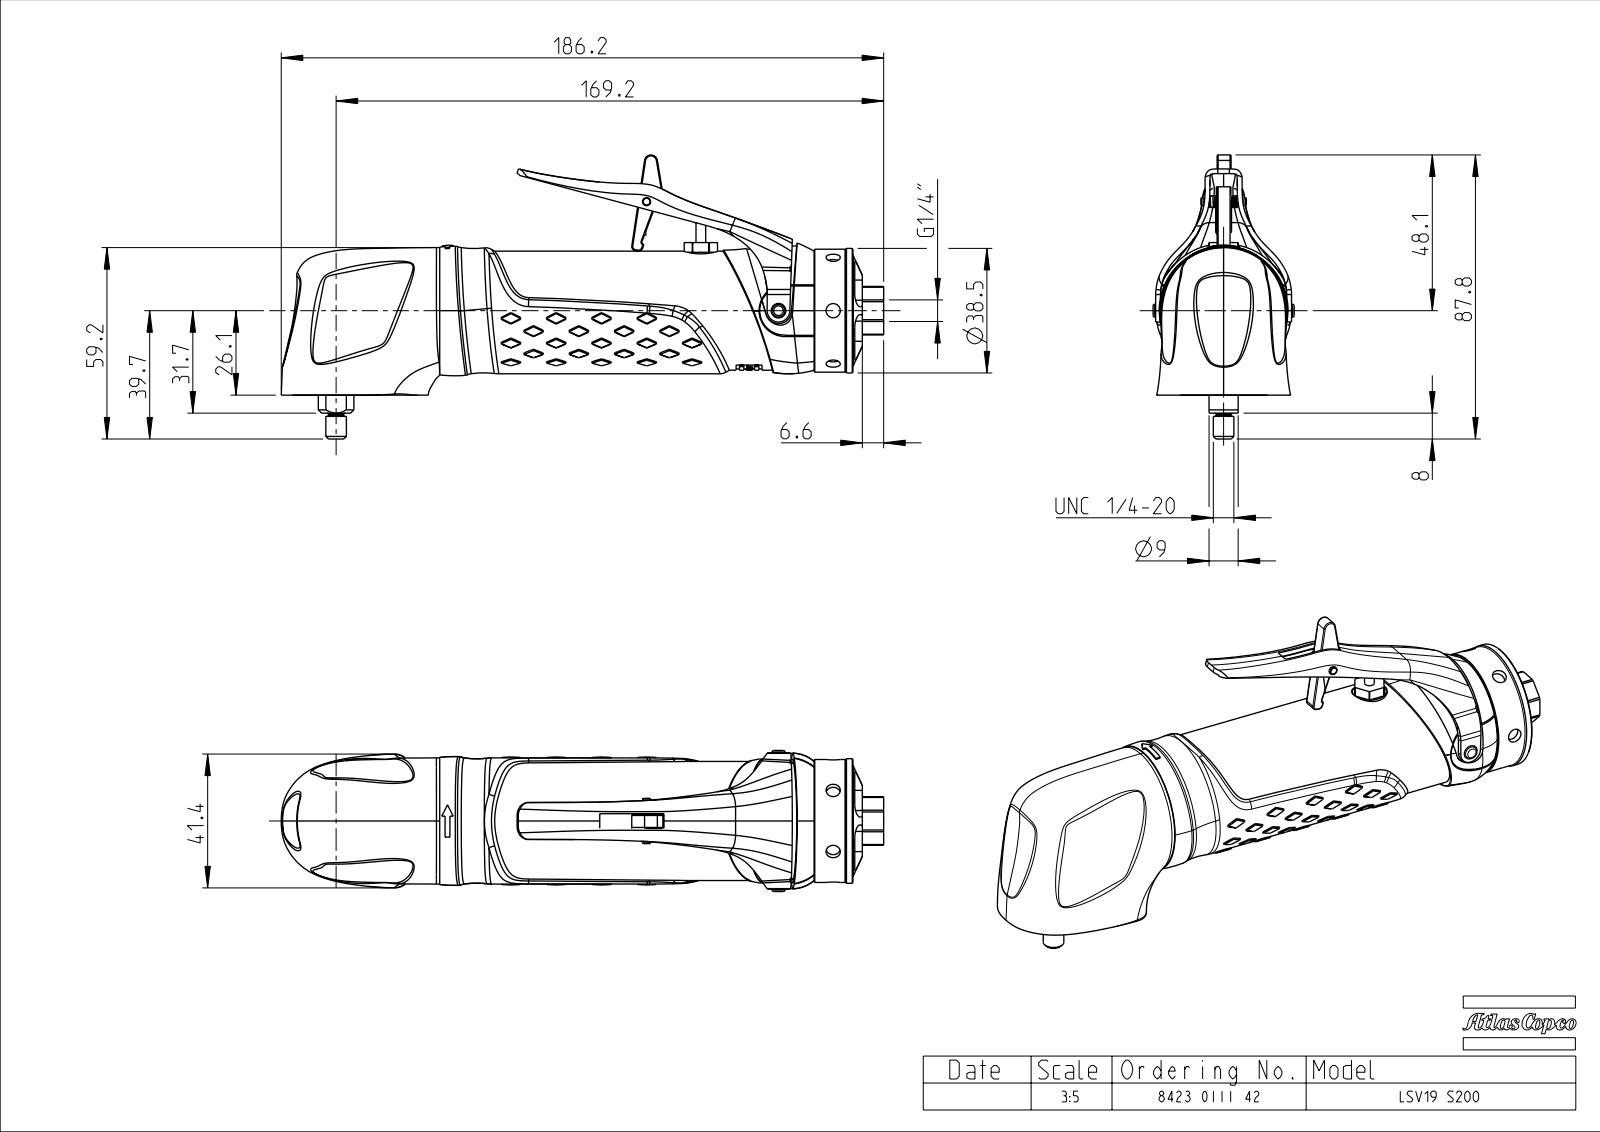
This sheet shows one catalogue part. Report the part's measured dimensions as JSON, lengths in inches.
{"part_name": "TMP1700_SW", "step_written_by": "PRO/ENGINEER BY PARAMETRIC TECHNOLOGY CORPORATION, 2011410 (CONFIG_CONTROL_DESIGN)", "units": "inches", "bodies": {"solids": 0, "faces": 639, "planar": 67, "cylindrical": 146, "other": 426}, "overall_size": [7.33, 3.457, 1.717], "round_holes": [[0.173, 3], [0.451, 1], [0.461, 1], [0.63, 1]], "round_bosses_or_shafts": [[1.535, 1], [1.516, 1], [1.496, 1], [1.449, 1], [0.433, 1], [0.25, 1], [0.118, 1]], "partial_cylinders_radius": [[0.012, 9], [0.118, 8], [0.039, 3], [0.02, 2], [0.051, 2], [0.157, 2], [0.03, 1], [0.079, 1]], "face_to_face_distances": [0.059, 0.591, 0.374, 0.169, 0.173, 0.114, 0.531, 0.118, 0.472, 0.217]}
